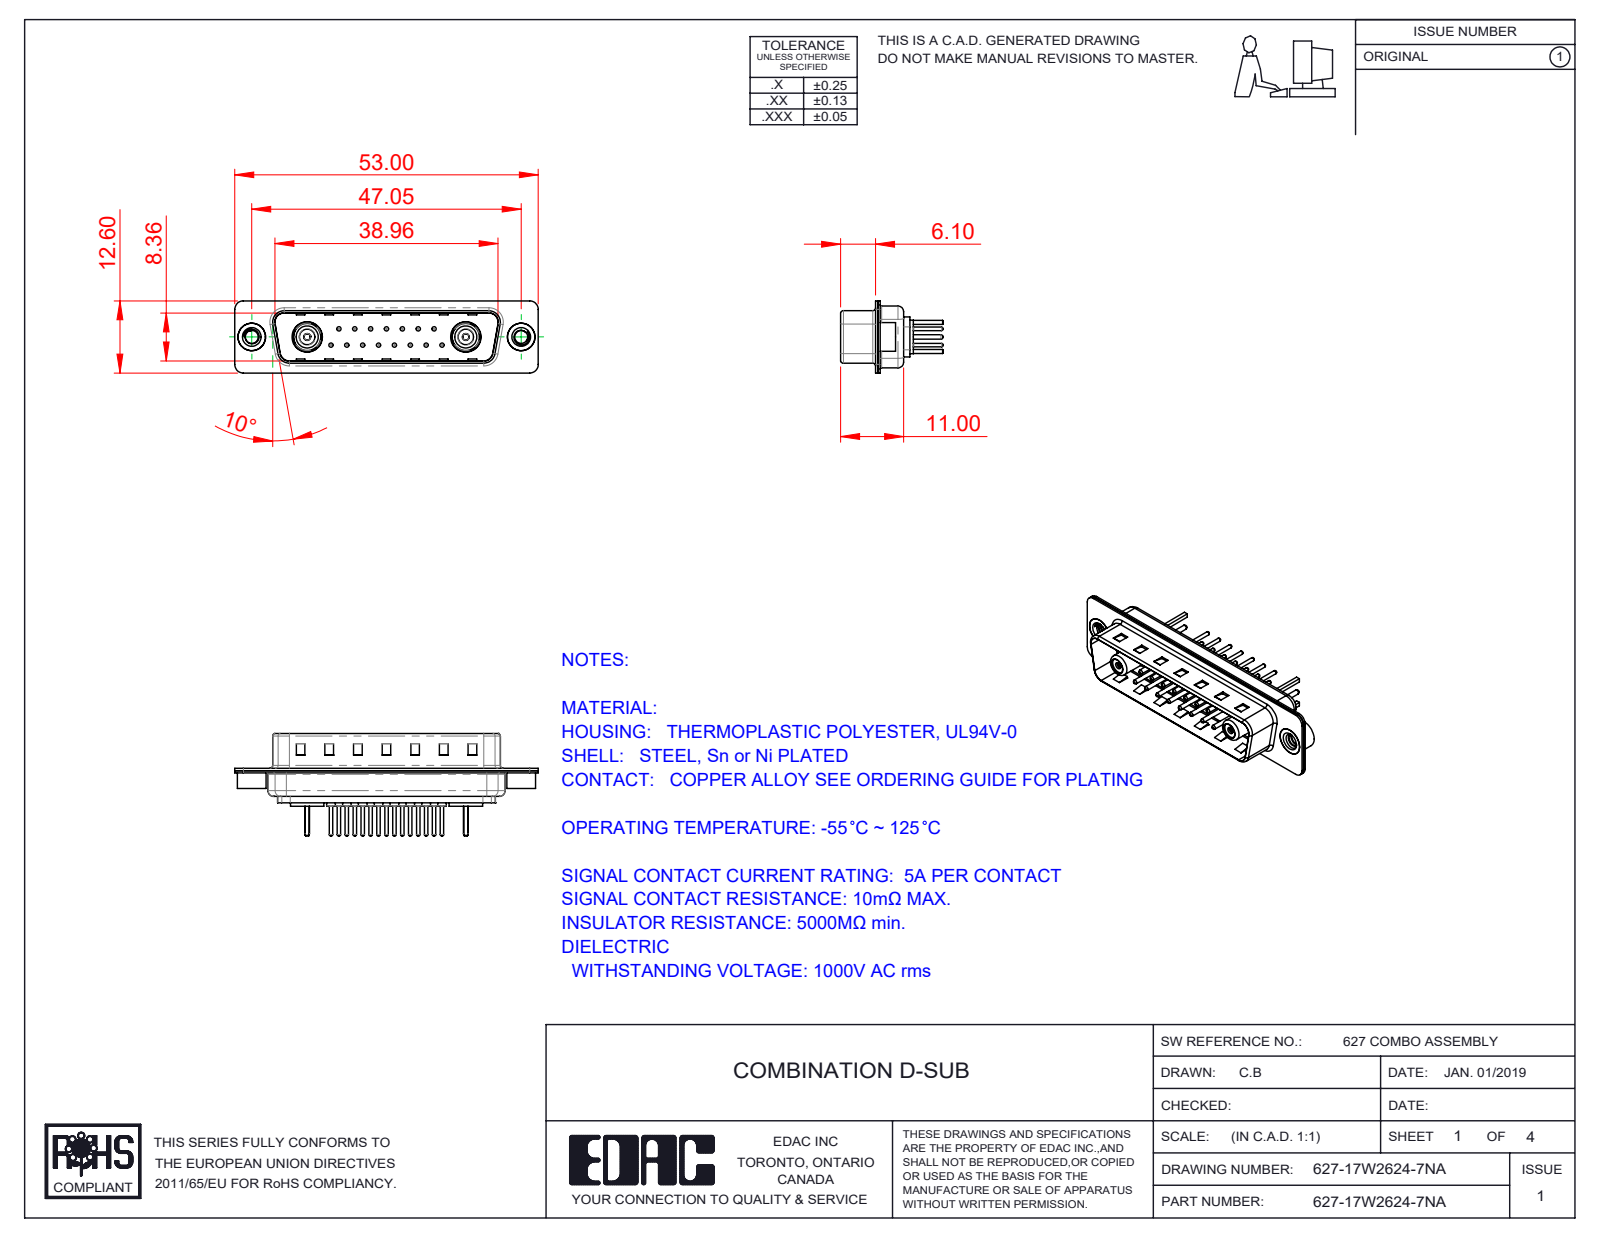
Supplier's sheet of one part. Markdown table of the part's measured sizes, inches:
| quantity | value |
| --- | --- |
| part name | Socket_Str; 627Combo Contact Row 2_24; 627Combo Threaded Rivet_A; Co-Ax Jack Assy_S (+8 more) |
| STEP written by | SolidWorks 2016 (CONFIG_CONTROL_DESIGN) |
| units | inches |
| bodies | 30 solids, 1152 faces (370 planar, 442 cylindrical, 340 other) |
| overall size | 2.087 × 0.705 × 0.496 |
| volume | 0.169 in³ |
| surface area | 11.77 in² |
| round holes (diameter × count) | 0.063 × 17, 0.03 × 15, 0.079 × 15, 0.043 × 2, 0.047 × 2, 0.059 × 2, 0.089 × 2, 0.098 × 2, 0.106 × 2, 0.134 × 2, 0.157 × 2, 0.189 × 2 |
| round bosses / shafts (diameter × count) | 0.059 × 15, 0.024 × 15, 0.23 × 2, 0.205 × 2, 0.197 × 2, 0.193 × 2, 0.189 × 2, 0.186 × 2 |
| partial cylindrical surfaces (radius × count) | 0.059 × 16, 0.079 × 12, 0.02 × 8, 0.063 × 8, 0.01 × 4, 0.024 × 4, 0.026 × 4, 0.035 × 4 |
| main face-to-face distances | 0.016, 0.032, 0.377, 0.345, 0.059, 0.236, 0.031, 0.22, 0.048, 0.393 |
| hole center spacings | 0.124, 0.109, 0.218, 0.327, 0.198, 0.295, 0.436, 0.198 |
